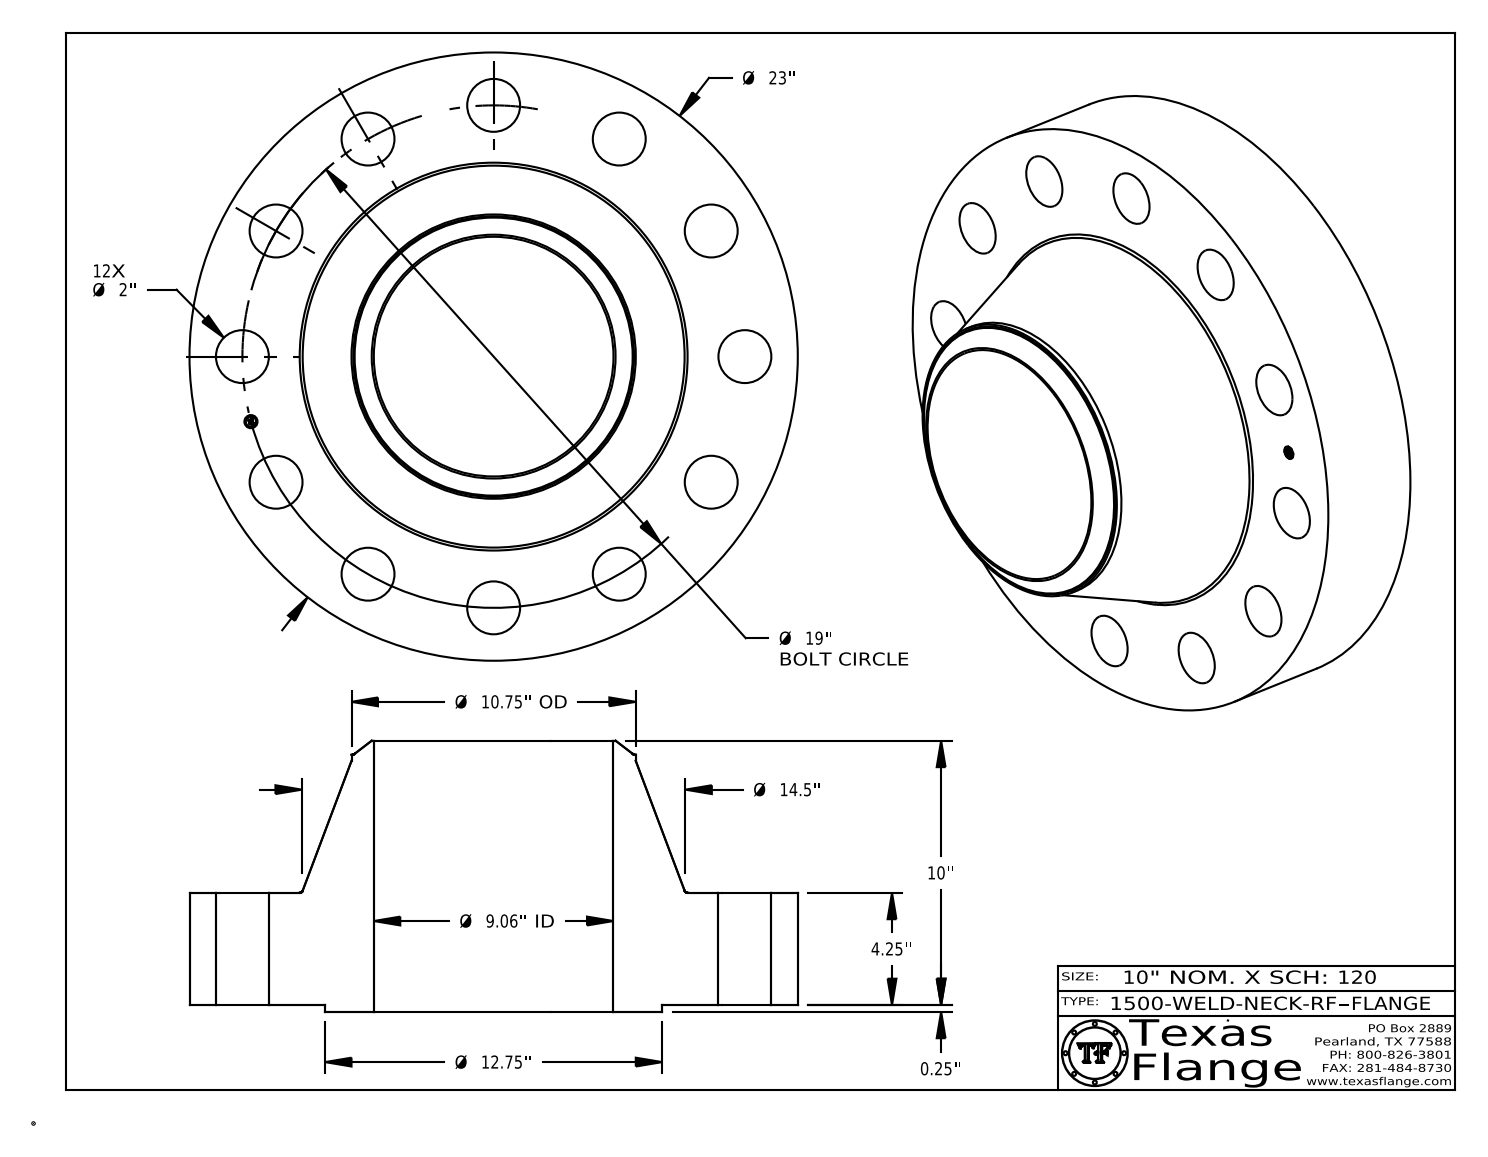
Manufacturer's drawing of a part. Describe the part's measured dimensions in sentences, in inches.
The part is named "1500-WELD-NECK-RF". Its 3-D file was written by "CATIA V5 STEP AP214 (AUTOMOTIVE_DESIGN)". It is 1 solid with 431 faces: 369 planar, 52 cylindrical and 10 other. Overall it measures 23 by 23 by 10.25 inches. Its volume is 1 667 cubic inches and its surface area 1 705 square inches. Round holes: 12 of diameter 2, 1 of diameter 0.495, 1 of diameter 9.062. Round bosses or shafts: 8 of diameter 0.03, 1 of diameter 23, 1 of diameter 12.75, 1 of diameter 10.75, 1 of diameter 0.39. The main face-to-face distances are 4.25, 0.25, 4.5, 10.25, 10, 5.75, 4.485, 4.235, 0.015, 5.765. The hole center spacings are 9.5, 13.435, 16.454, 18.352, 4.918, 19, 4.917, 15.074.
